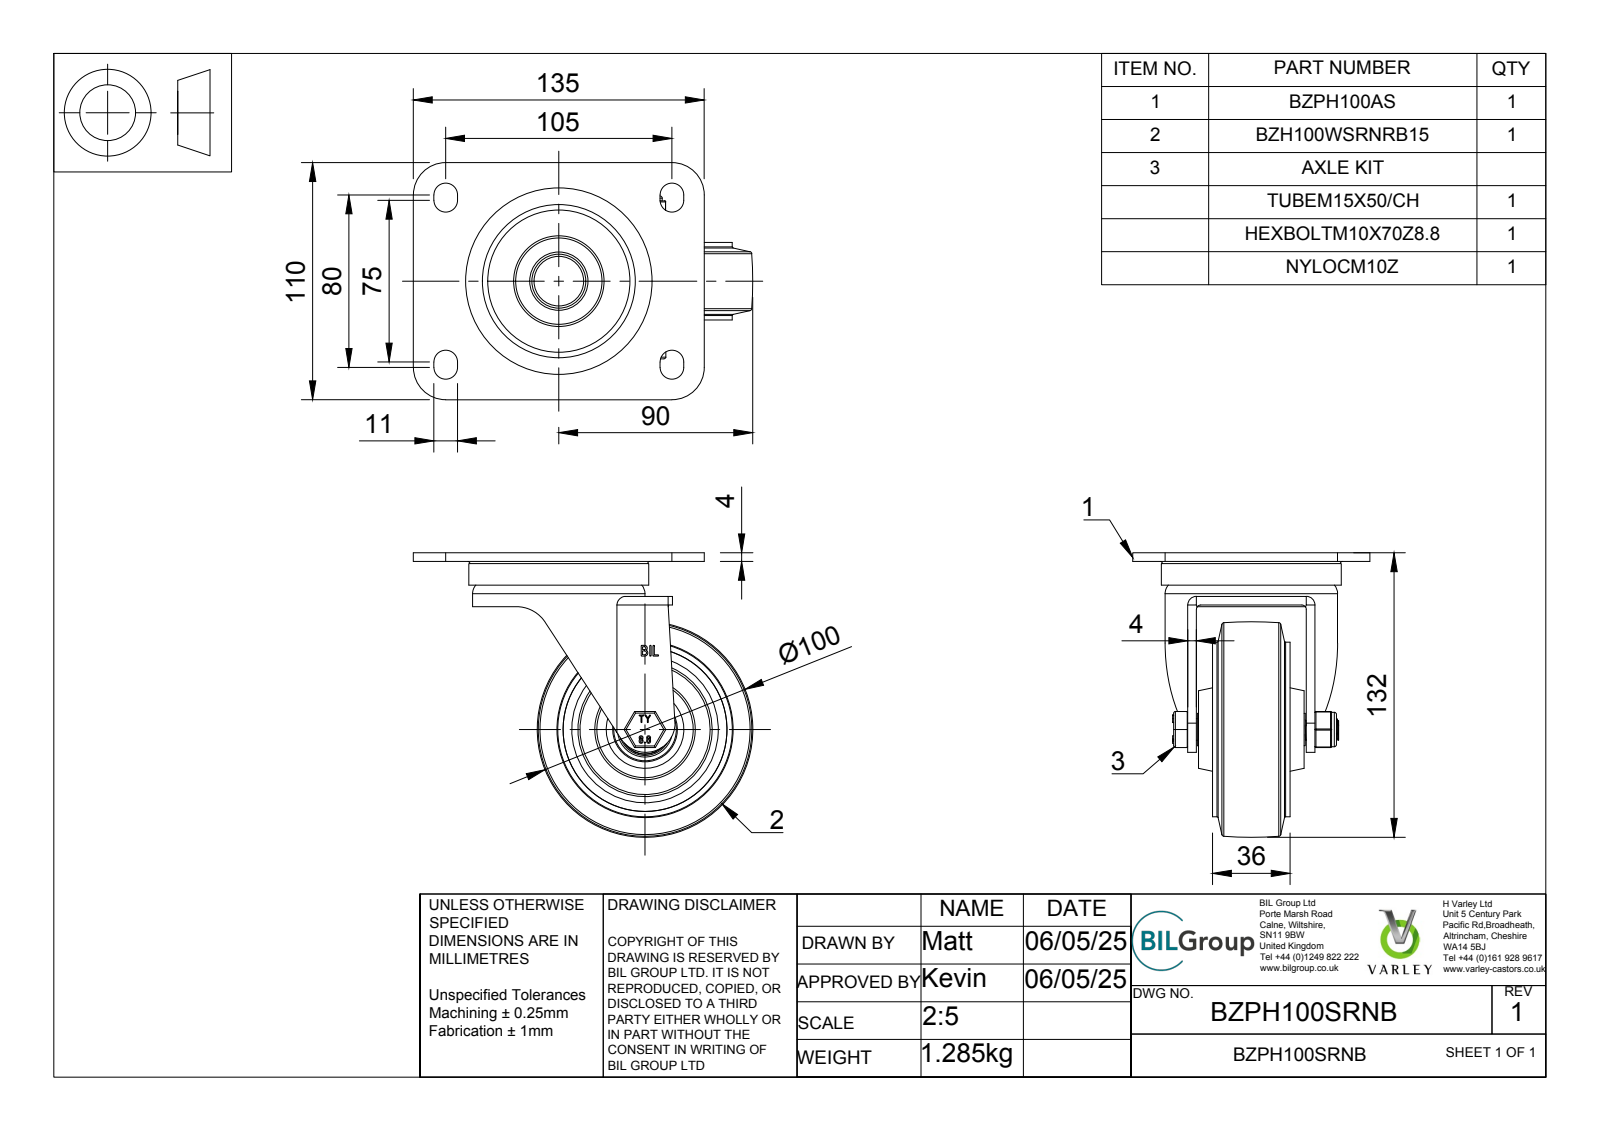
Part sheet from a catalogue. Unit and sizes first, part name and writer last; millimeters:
Units: millimetres
Overall size (bounding box): 157.5 × 132 × 110
Round holes (diameter × count): ⌀10 ×1, ⌀10.2 ×1, ⌀10.5 ×1, ⌀12 ×1, ⌀15 ×1, ⌀23 ×1, ⌀26 ×1, ⌀28 ×1, ⌀30 ×1, ⌀72 ×1, ⌀76 ×1, ⌀82.5 ×1
Round bosses / shafts (diameter × count): ⌀4 ×8, ⌀83.5 ×1, ⌀81 ×1, ⌀80 ×1, ⌀51 ×1, ⌀32 ×1, ⌀25 ×1, ⌀22.75 ×1
Partial cylindrical surfaces — rounded edges, fillets, slot ends (radius × count): R0.5 ×18, R5.5 ×8, R0.75 ×6, R2 ×4, R15 ×4, R4 ×2, R9.38 ×1, R13.6 ×1
Main face-to-face distances: 4, 9, 13, 21, 15, 11.5, 55, 7.5, 47.5, 43.5
Volume: 364 049 mm³ · Surface area: 148 929 mm²
Bodies: 19 solids, 491 faces (251 planar, 144 cylindrical, 96 other)
Part name (STEP PRODUCT): BZPH100SRNB v3; BZPH100AS v1; ZINC PLATED, PRESSED STEEL TOP PLATE; ZINC PLATED, PRESSED STEEL FORKS (+7 more)
STEP written by: Autodesk Translation Framework v14.4.0.0 (AUTOMOTIVE_DESIGN)
